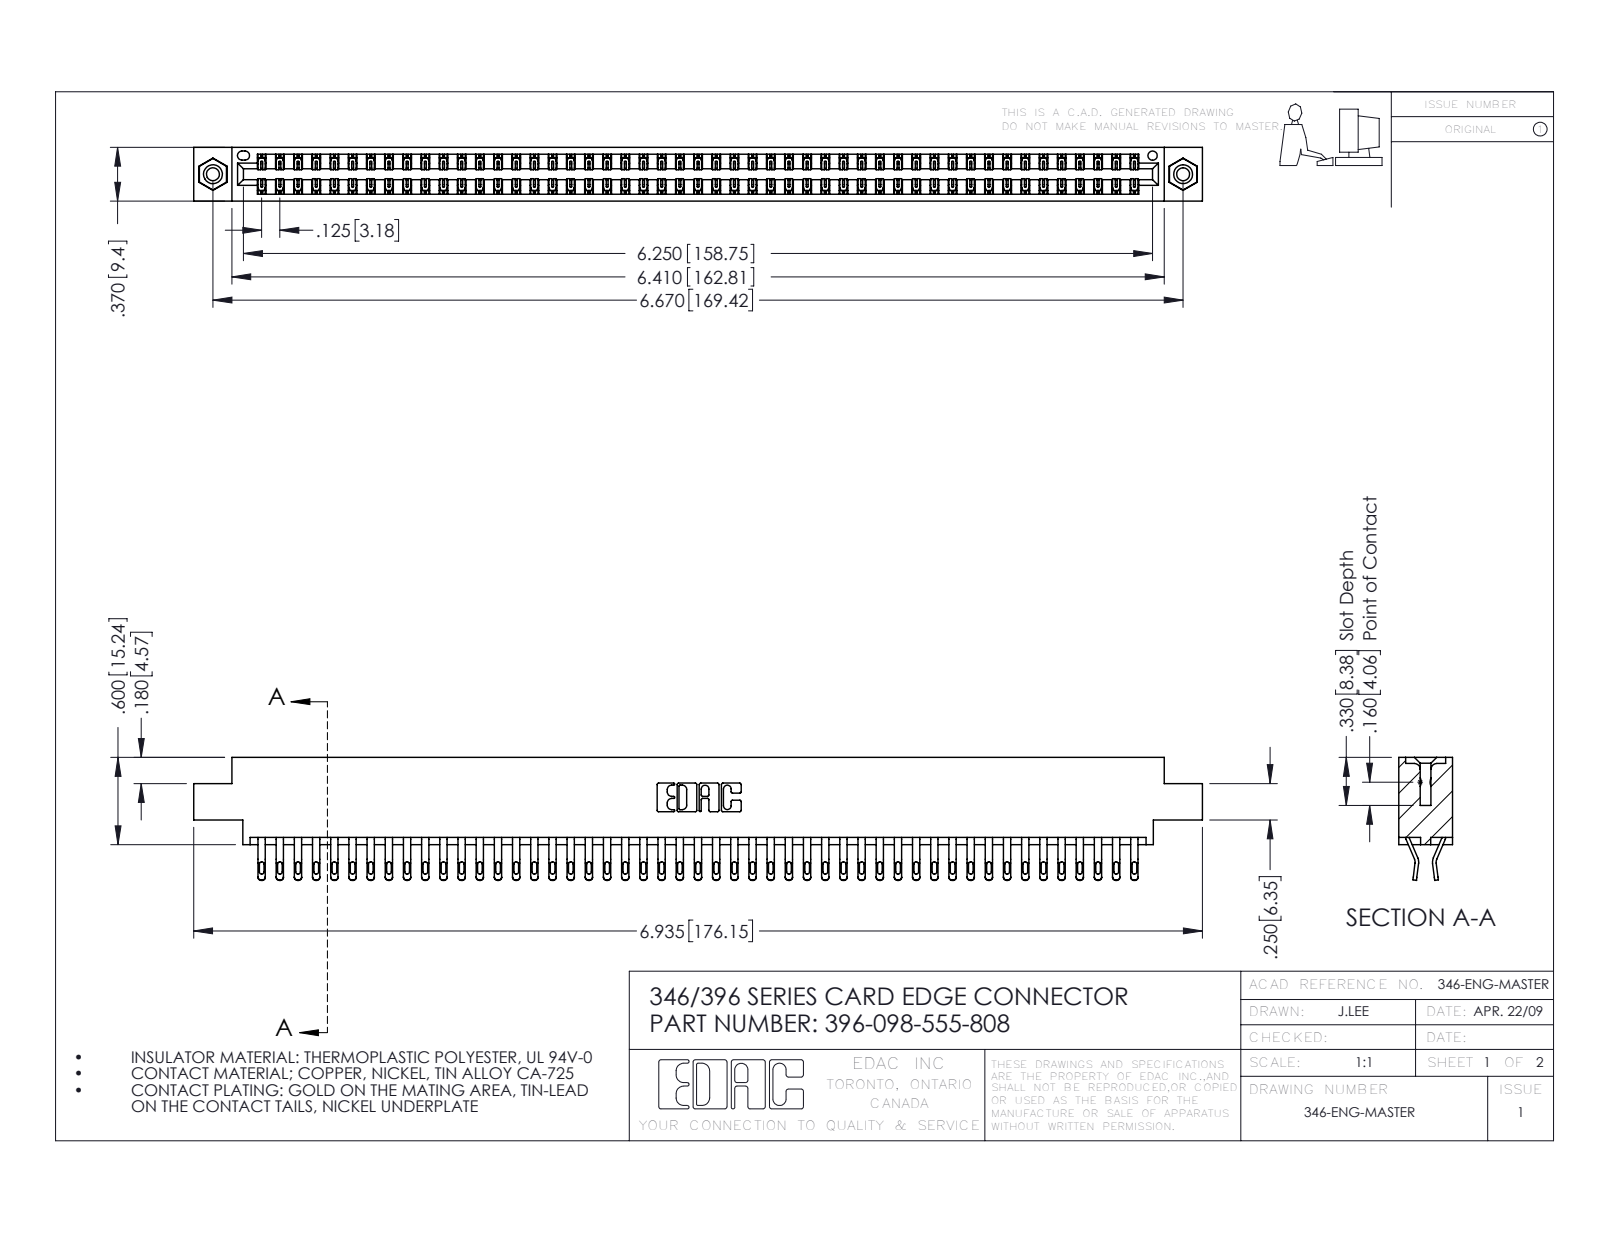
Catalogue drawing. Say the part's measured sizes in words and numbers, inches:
The part is named "345-250-001_345-250-003-102; 346 Part_0.170 Offset - 0.156 Dia-TI; 396-098-555-808; 345-292-001_555 Tail". Its 3-D file was written by "SolidWorks 2016 (CONFIG_CONTROL_DESIGN)". It is 101 solids with 5870 faces: 3346 planar, 2508 cylindrical and 16 other. Overall it measures 6.935 by 0.845 by 0.37 inches. Its volume is 1.059 cubic inches and its surface area 39.03 square inches. Round holes: 2 of diameter 0.089, 2 of diameter 0.125, 2 of diameter 0.156, 1 of diameter 0.064. Round bosses or shafts: 2 of diameter 0.155. Partial cylindrical surfaces (rounded edges, fillets, slot ends): 196 of radius 0.016, 196 of radius 0.02, 147 of radius 0.006, 22 of radius 0.01, 6 of radius 0.007, 6 of radius 0.031, 3 of radius 0.026, 2 of radius 0.01. The main face-to-face distances are 0.048, 0.322, 0.37, 0.25, 0.025, 0.072, 0.298, 0.275, 0.222, 0.148. The hole center spacings are 0.246, 6.461, 6.67.
